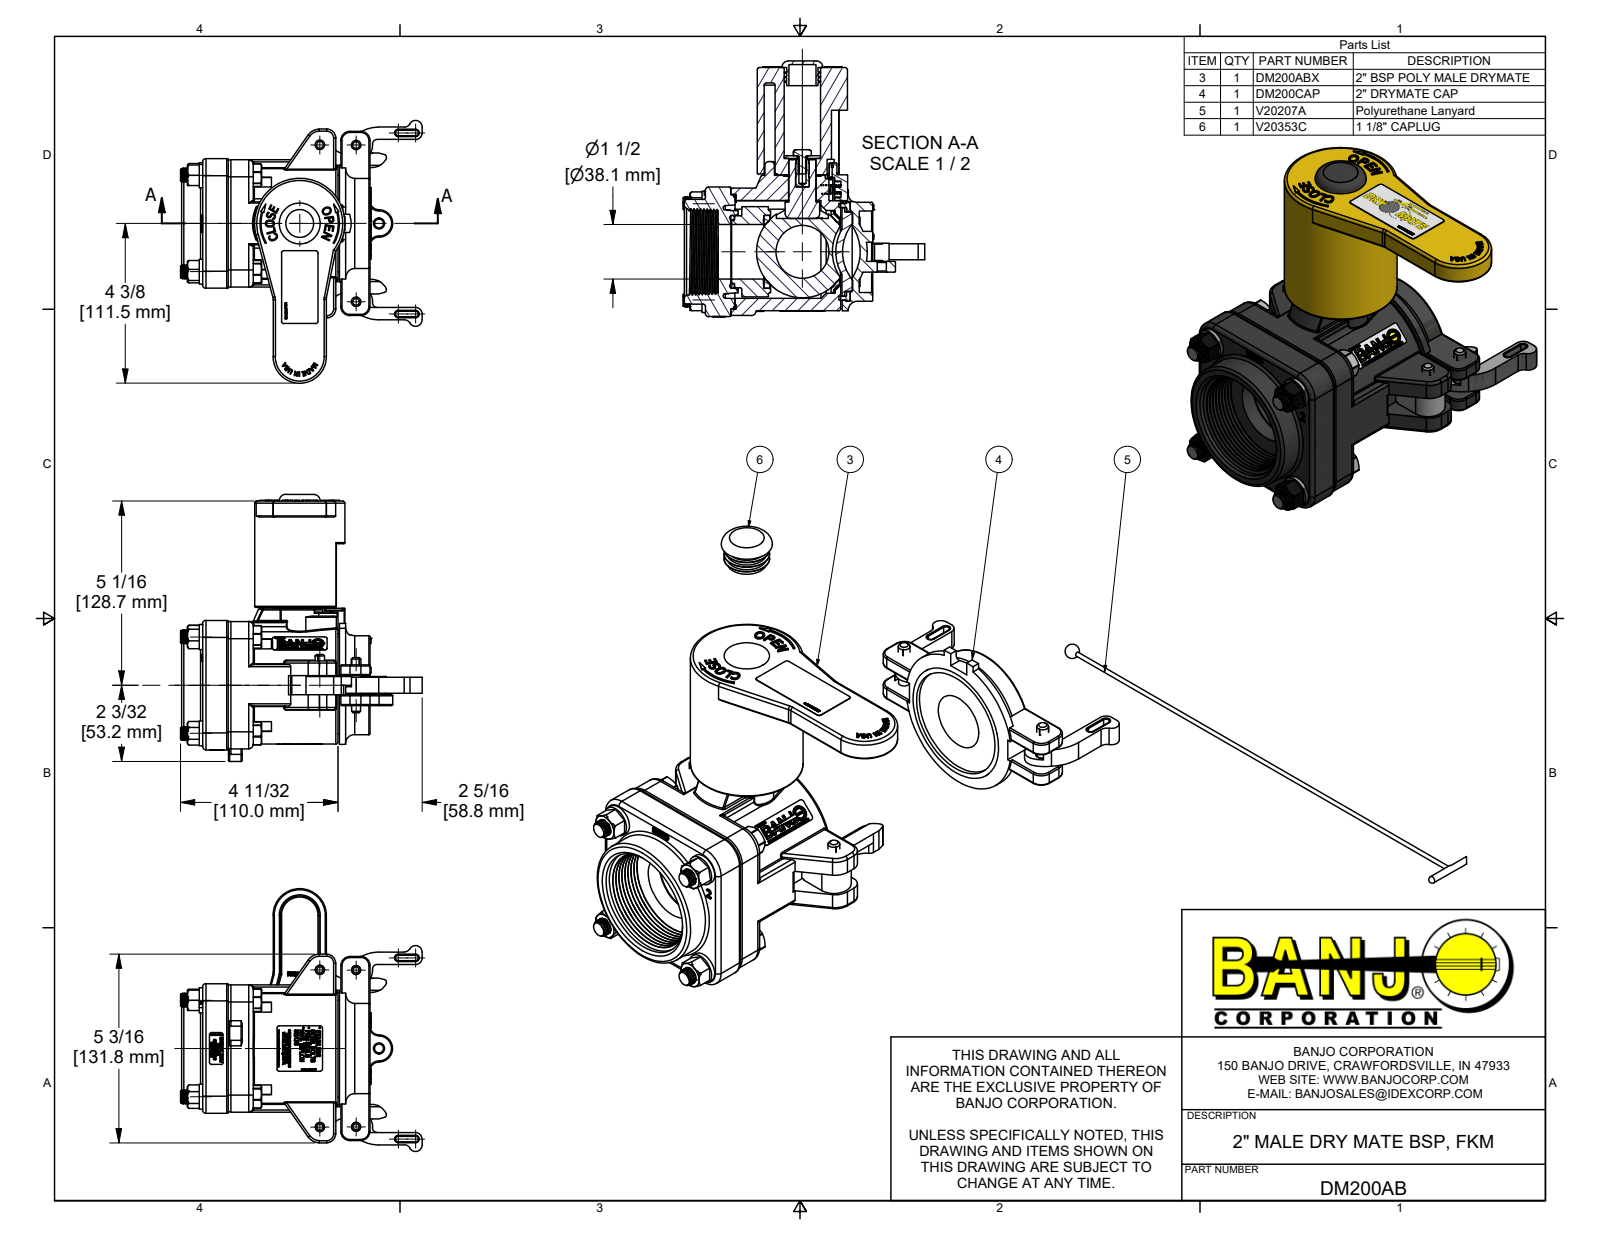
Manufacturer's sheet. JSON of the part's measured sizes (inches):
{"part_name": "DM200AB; DM200ABX; DM20254; DM20254MY (+8 more)", "step_written_by": "Autodesk Inventor 2022 (AUTOMOTIVE_DESIGN)", "units": "inches", "bodies": {"solids": 46, "faces": 6632, "planar": 3271, "cylindrical": 892, "other": 2469}, "overall_size": [7.34, 7.22, 6.646], "volume_in3": 49.81, "surface_area_in2": 430.2, "round_holes": [[0.406, 8], [0.25, 5], [0.375, 5], [0.256, 4], [0.307, 4], [0.385, 4], [0.125, 3], [0.196, 1], [0.2, 1], [0.227, 1], [0.281, 1], [0.321, 1]], "round_bosses_or_shafts": [[0.324, 60], [0.687, 4], [0.375, 4], [0.26, 4], [0.249, 4], [0.28, 3], [2.48, 2], [3.25, 1]], "partial_cylinders_radius": [[0.03, 104], [0.06, 56], [0.02, 20], [0.01, 12], [0.125, 10], [0.25, 10], [0.09, 8], [0.162, 8]], "face_to_face_distances": [0.298, 3.53, 3.02, 3.28, 0.035, 0.7, 3.72, 0.297, 0.03, 0.35], "hole_center_spacings": [2.653, 1.872, 1.88, 2.648, 2.658, 3.752, 0.95, 1.646]}
